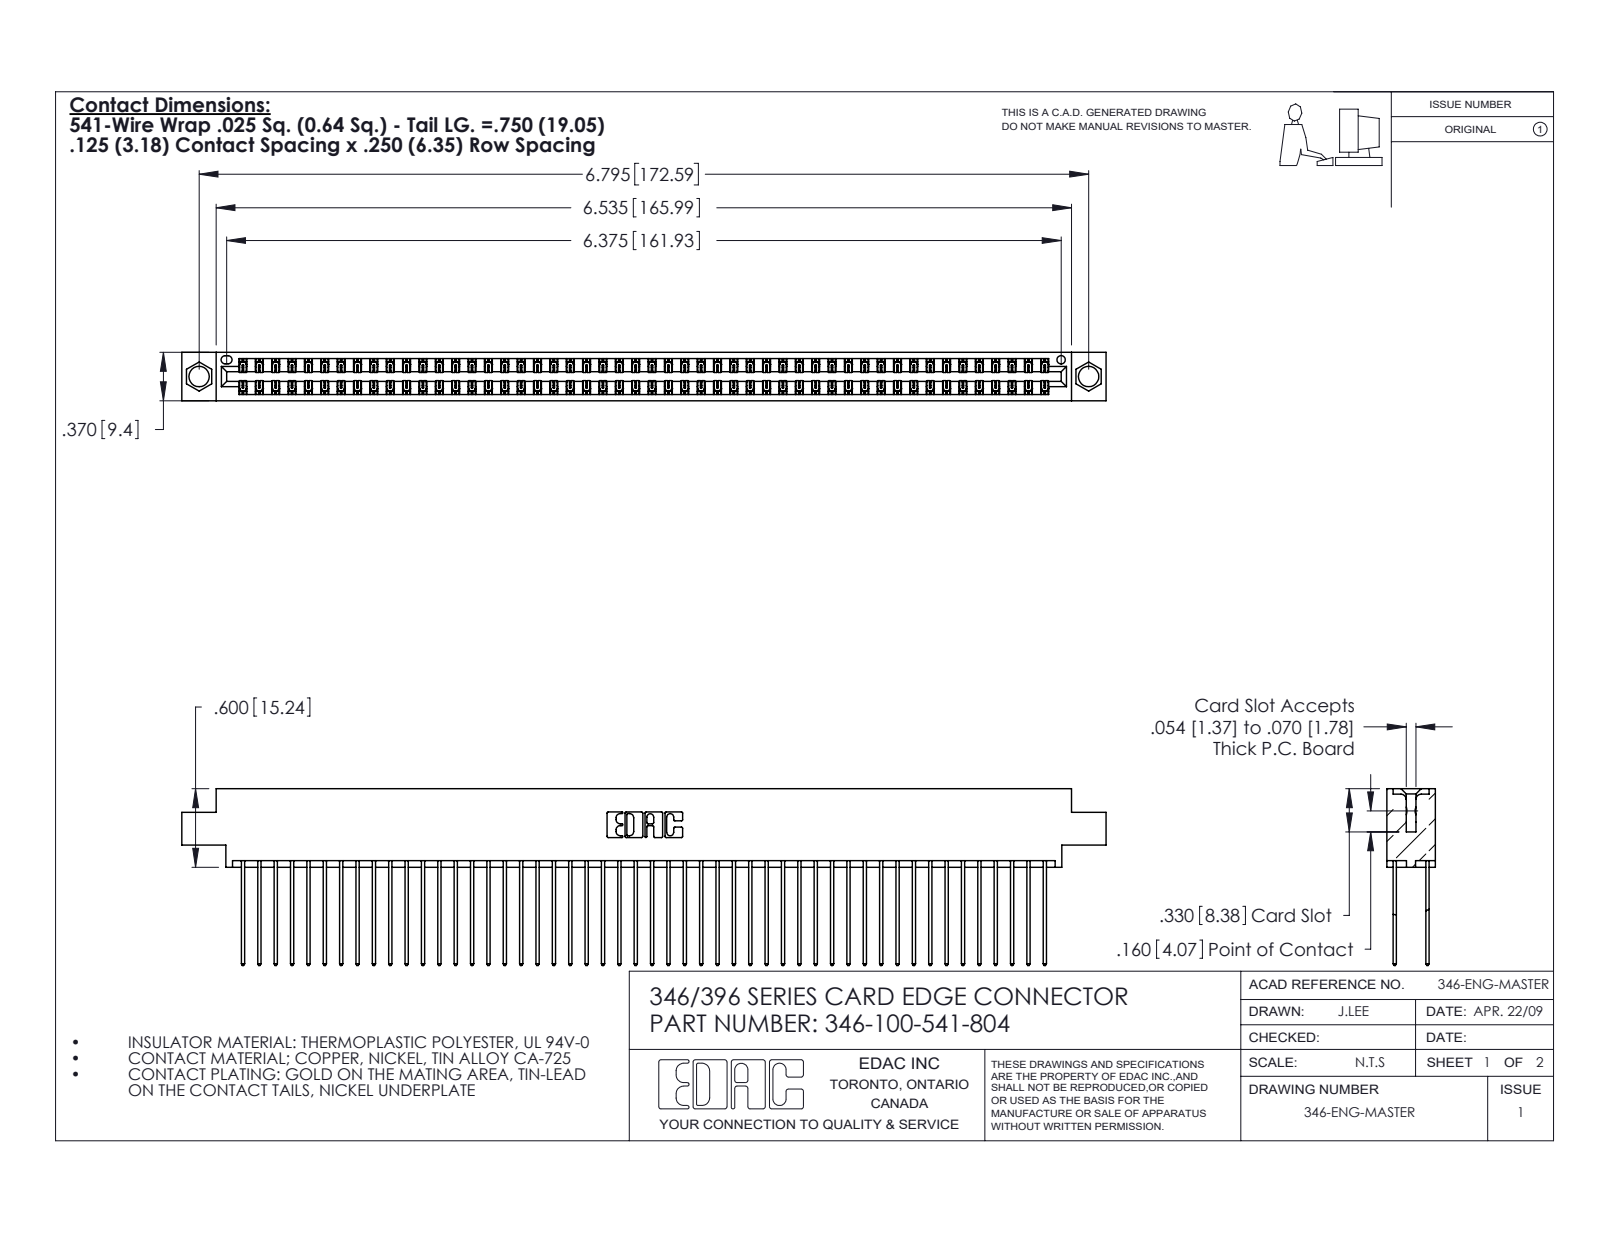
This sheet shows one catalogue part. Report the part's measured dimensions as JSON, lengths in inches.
{"part_name": "346-100-541-804; 346 Part_0.170 Offset - 0.156 Dia-TH; 345-292-001_345-293-141", "step_written_by": "SolidWorks 2020 (CONFIG_CONTROL_DESIGN)", "units": "inches", "bodies": {"solids": 101, "faces": 5340, "planar": 3594, "cylindrical": 1746, "other": 0}, "overall_size": [7.06, 1.35, 0.37], "volume_in3": 1.09, "surface_area_in2": 42.56, "round_holes": [[0.156, 2], [0.064, 1]], "partial_cylinders_radius": [[0.006, 150], [0.01, 100], [0.01, 22], [0.007, 6], [0.031, 6], [0.026, 3], [0.014, 2], [0.022, 2]], "face_to_face_distances": [0.048, 0.322, 0.25, 0.072, 0.298, 0.025, 0.37, 0.275, 0.225, 0.222], "hole_center_spacings": [0.246, 6.586, 6.795]}
